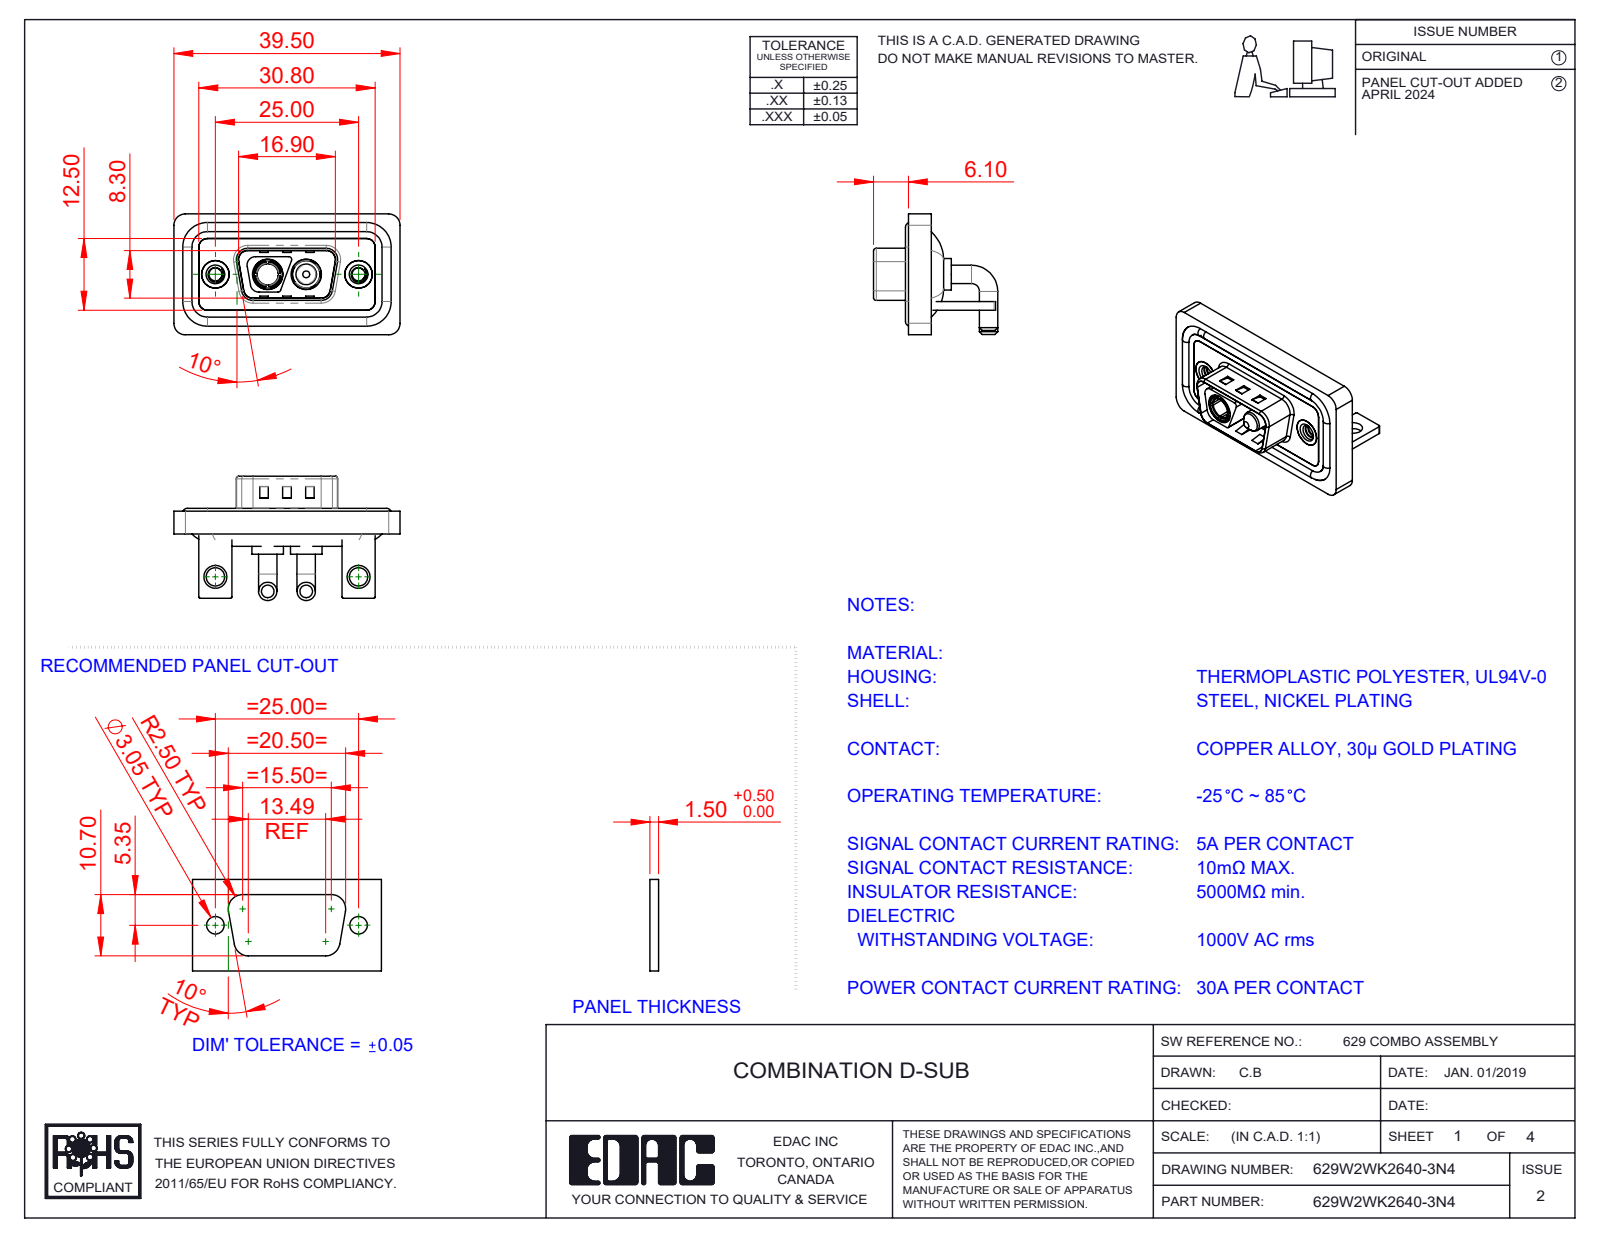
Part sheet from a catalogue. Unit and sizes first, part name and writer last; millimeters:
Units: millimetres
Overall size (bounding box): 39.5 × 21.7 × 21.1
Round holes (diameter × count): ⌀2.26 ×2, ⌀3.2 ×2, ⌀4 ×2, ⌀4.8 ×2, ⌀4.85 ×2, ⌀5 ×2, ⌀5.3 ×2, ⌀3.7 ×1
Round bosses / shafts (diameter × count): ⌀3.2 ×4, ⌀1.6 ×4, ⌀5.5 ×2, ⌀5.2 ×2, ⌀4.9 ×2, ⌀4.75 ×2, ⌀3.75 ×2, ⌀4.96 ×1
Partial cylindrical surfaces — rounded edges, fillets, slot ends (radius × count): R1.5 ×20, R2 ×19, R0.25 ×16, R0.5 ×11, R1.6 ×8, R0.6 ×4, R0.65 ×4, R0.9 ×4
Main face-to-face distances: 0.4, 1.5, 2.9, 0.8, 1.1, 1.2, 2.1, 1.6, 3.7, 2.5
Hole centre spacings: 9.14, 15.86, 25, 6.72
Volume: 5 017 mm³ · Surface area: 8 157 mm²
Bodies: 13 solids, 582 faces (209 planar, 249 cylindrical, 124 other)
Part name (STEP PRODUCT): Power Socket_30A RA; 629Combo Stabilizer Bracket; 629Combo Shell Front_09 Contacts; 629Combo Waterproof Housing_09 Contacts (+5 more)
STEP written by: SolidWorks 2023 (CONFIG_CONTROL_DESIGN)
